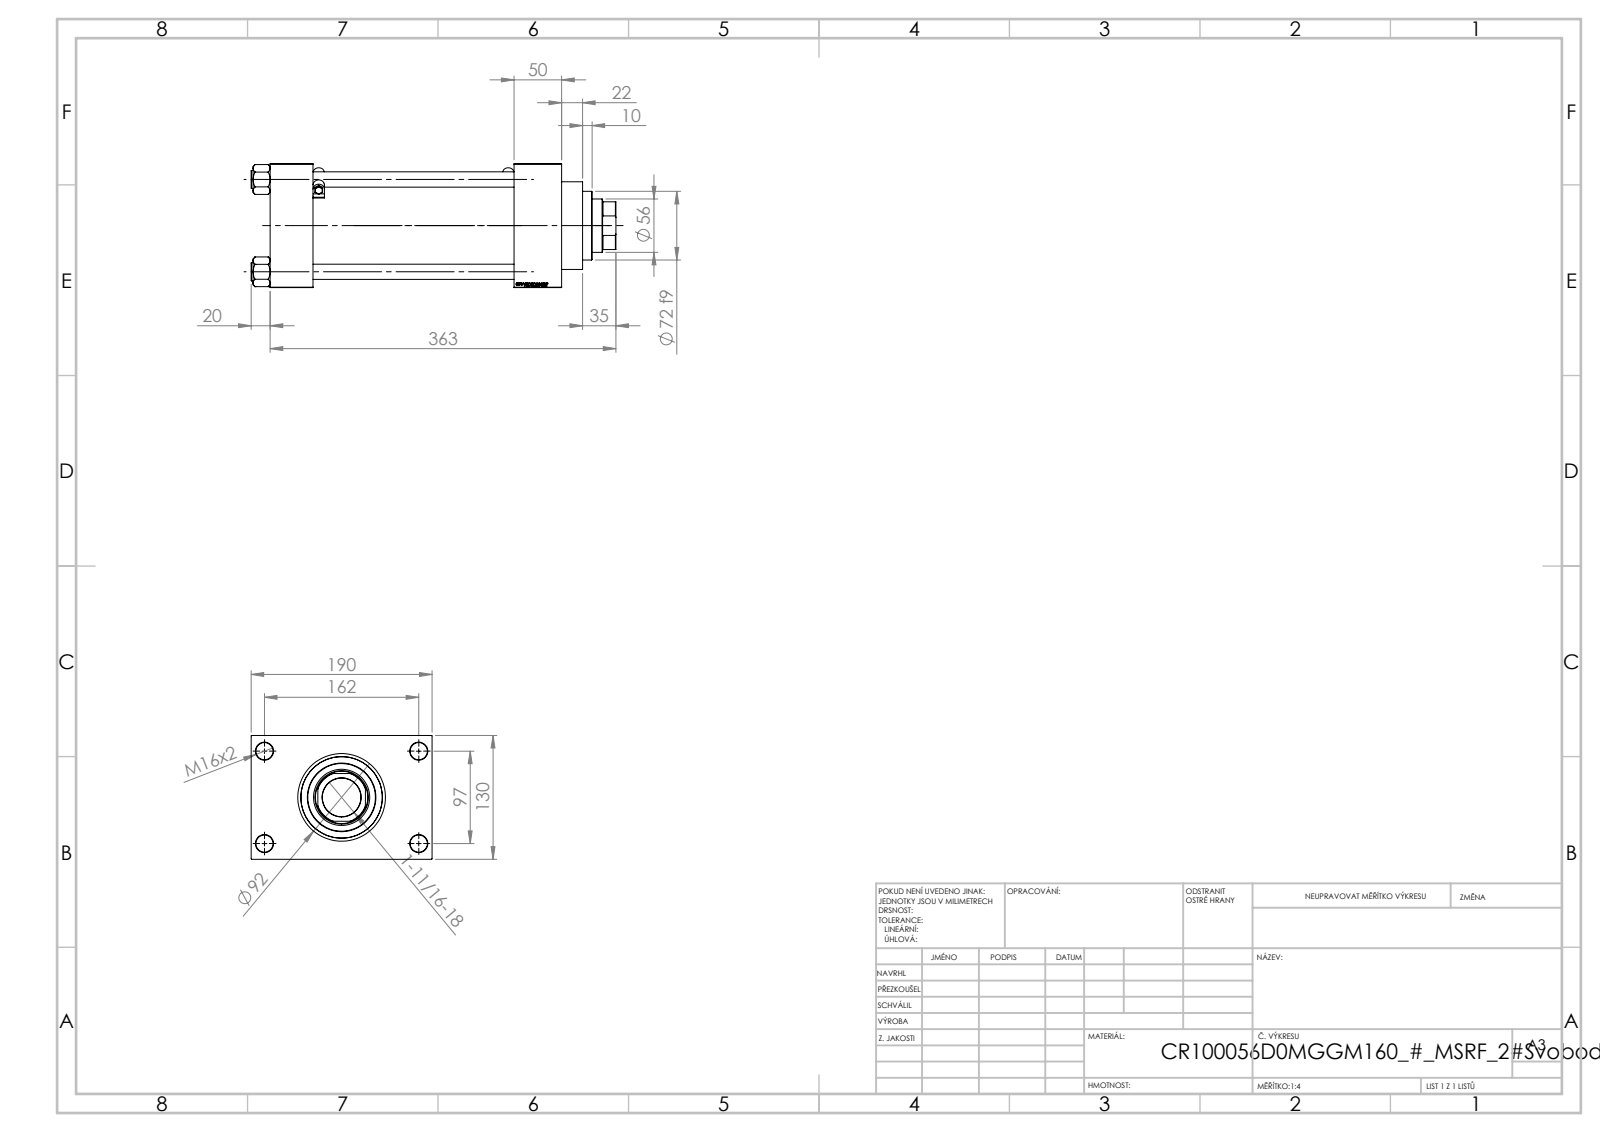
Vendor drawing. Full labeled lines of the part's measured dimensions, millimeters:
Part name (STEP PRODUCT): V215CR_VCP_D; V215_VC_A; MSRF_MSRG1; V215CR_D_Body (+2 more)
STEP written by: SolidWorks 2019 (CONFIG_CONTROL_DESIGN)
Units: millimetres
Bodies: 13 solids, 1216 faces (581 planar, 117 cylindrical, 518 other)
Overall size (bounding box): 383 × 190 × 130
Volume: 3 245 000 mm³ · Surface area: 507 971 mm²
Round holes (diameter × count): ⌀16 ×4, ⌀18 ×4, ⌀7 ×2, ⌀26.44 ×2, ⌀35 ×2, ⌀40.5 ×1, ⌀56 ×1, ⌀59 ×1, ⌀76 ×1, ⌀85.5 ×1, ⌀100 ×1
Round bosses / shafts (diameter × count): ⌀19 ×4, ⌀5 ×2, ⌀2.5 ×2, ⌀106 ×1, ⌀92 ×1, ⌀72 ×1
Partial cylindrical surfaces — rounded edges, fillets, slot ends (radius × count): R0.5 ×12, R6 ×4, R27 ×1
Main face-to-face distances: 130, 50, 45, 256, 211, 306, 160, 261, 30, 190
Hole centre spacings: 32.55, 68.52, 94.41, 96.9, 102.27, 129.45, 161.73, 97
